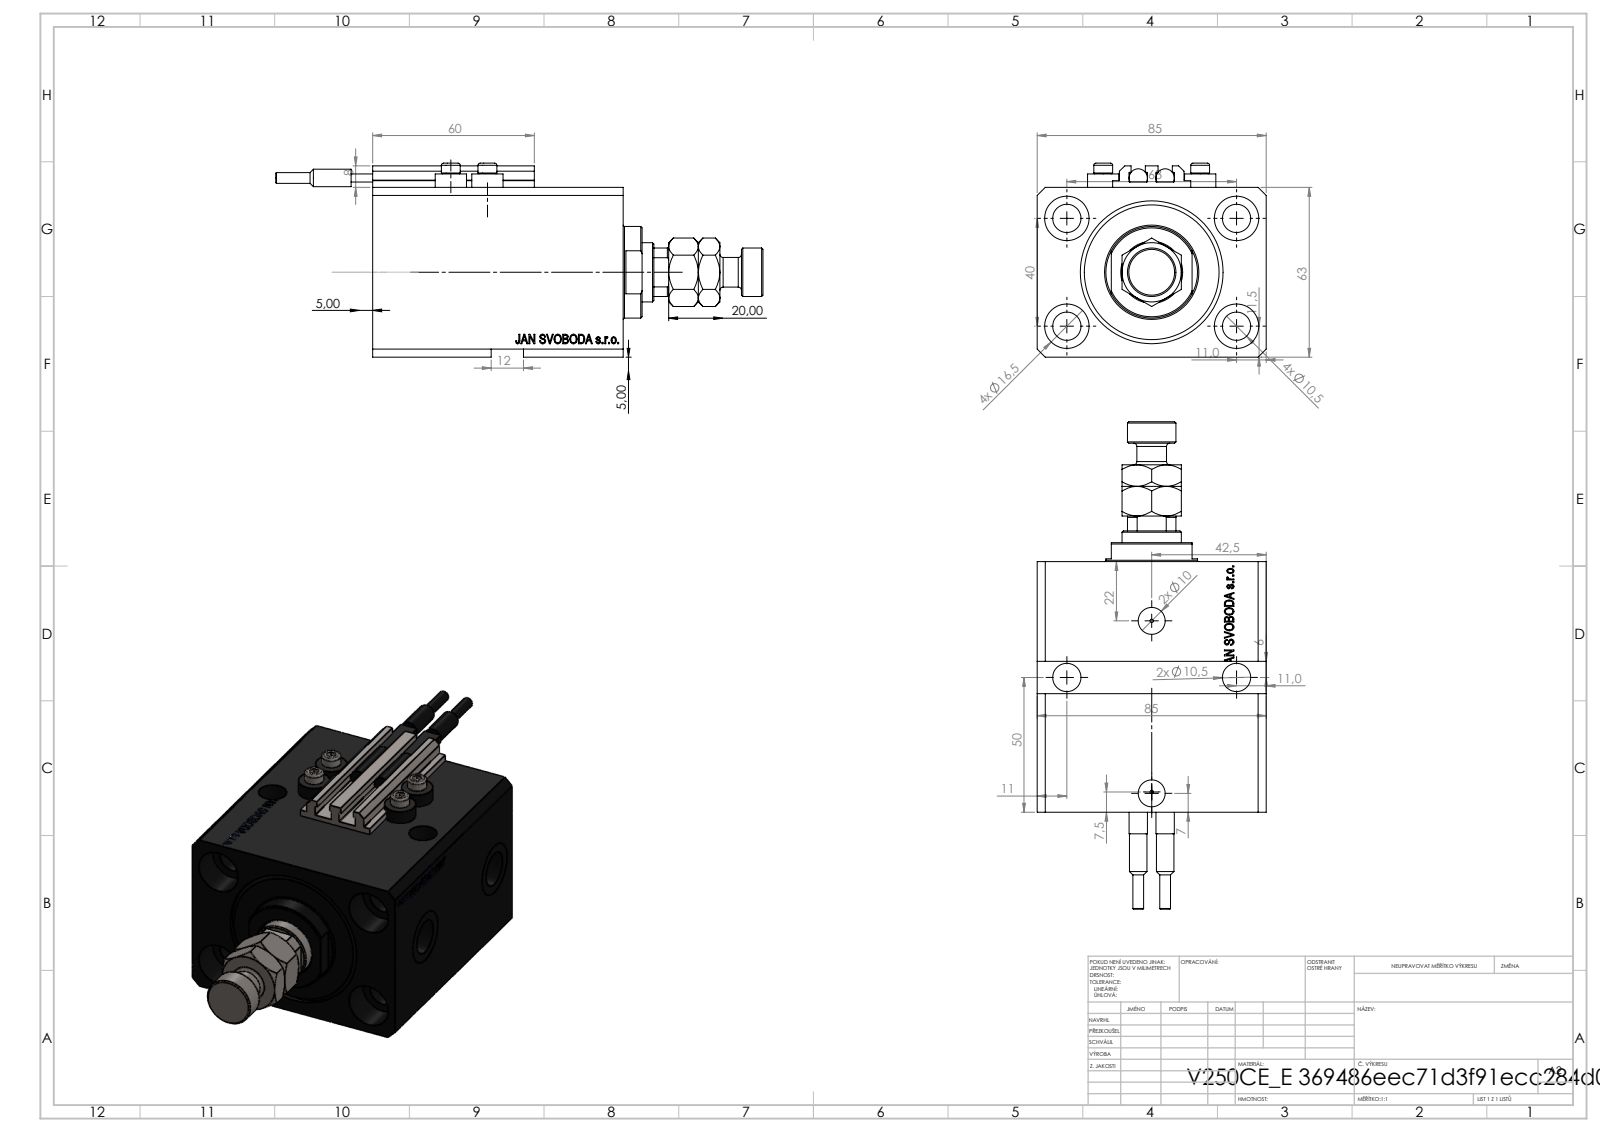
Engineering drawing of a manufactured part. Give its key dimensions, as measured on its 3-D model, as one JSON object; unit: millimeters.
{"part_name": "MFA; V250CE_VC_E; V250CE_E_Body; SWITCH_V250CE (+2 more)", "step_written_by": "SolidWorks 2019 (CONFIG_CONTROL_DESIGN)", "units": "millimeters", "bodies": {"solids": 11, "faces": 1191, "planar": 583, "cylindrical": 142, "other": 466}, "overall_size": [181, 85, 72], "volume_mm3": 451514, "surface_area_mm2": 101767, "round_holes": [[10.5, 6], [1.25, 4], [4, 4], [16.5, 4], [10, 2], [13.16, 2], [20, 2], [12.5, 1], [22, 1], [40, 1], [53, 1]], "round_bosses_or_shafts": [[11.6, 4], [7, 4], [6.8, 2], [6.5, 2], [4, 2], [34, 1], [18, 1], [11, 1]], "partial_cylinders_radius": [[0.2, 10], [10.5, 1]], "face_to_face_distances": [63, 85, 93, 17, 76, 11.4, 64.6, 81.6, 3, 65], "hole_center_spacings": [37.31, 63, 13.6, 15.4, 24.96, 28.02, 28.43, 33.62]}
